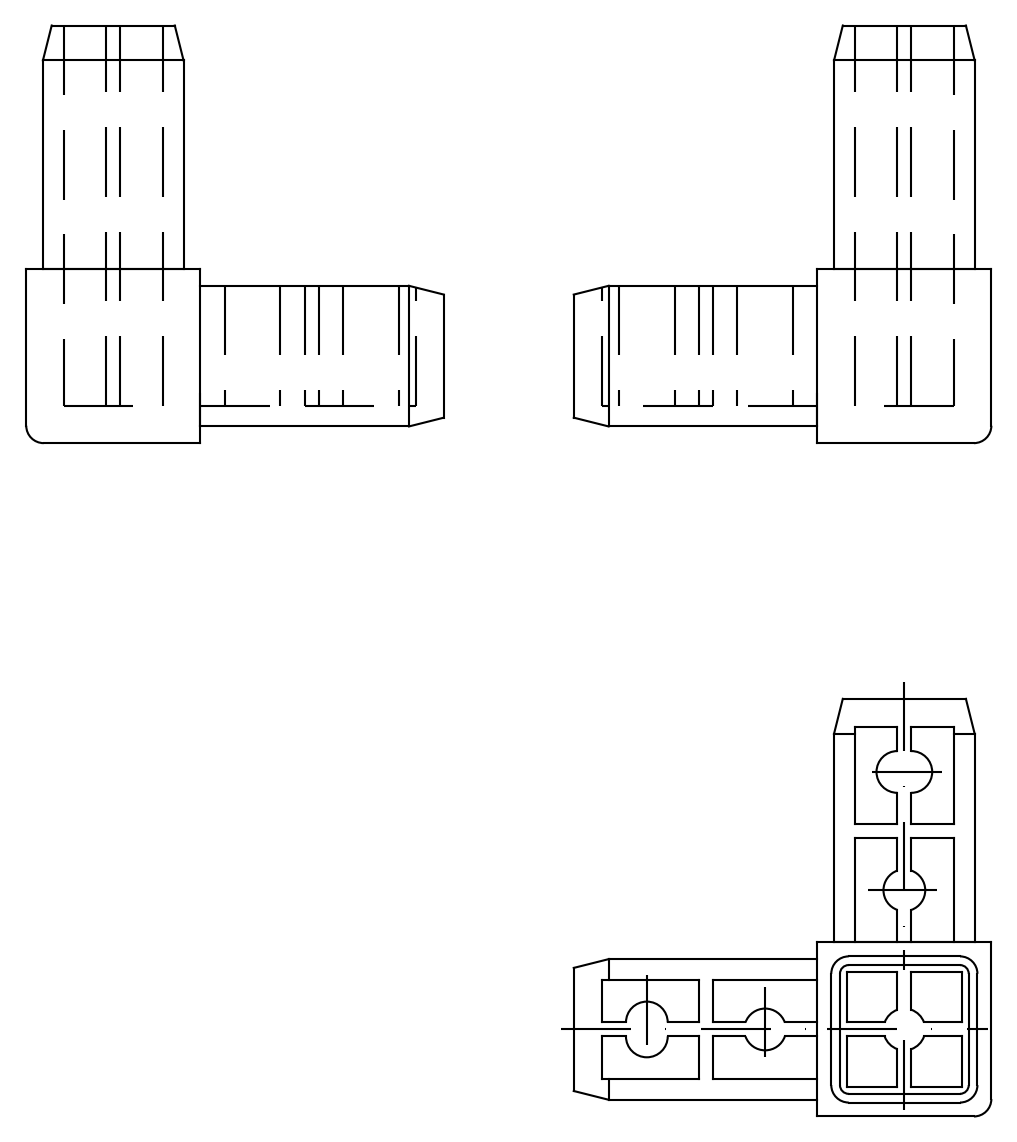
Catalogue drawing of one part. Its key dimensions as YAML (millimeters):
step_written_by: "THINKDESIGN (CONFIG_CONTROL_DESIGN)"
units: millimeters
bodies: {solids: 1, faces: 137, planar: 85, cylindrical: 27, other: 25}
overall_size: [60, 60, 60]
volume: 40525
surface_area: 21438
partial_cylinders:
  - {radius: 2.5, count: 13}
  - {radius: 3, count: 7}
  - {radius: 5, count: 2}
face_to_face_distances: [11.5, 2, 2.4, 22.6, 3, 5.4, 19.6, 17.2, 7.25, 9.25]
